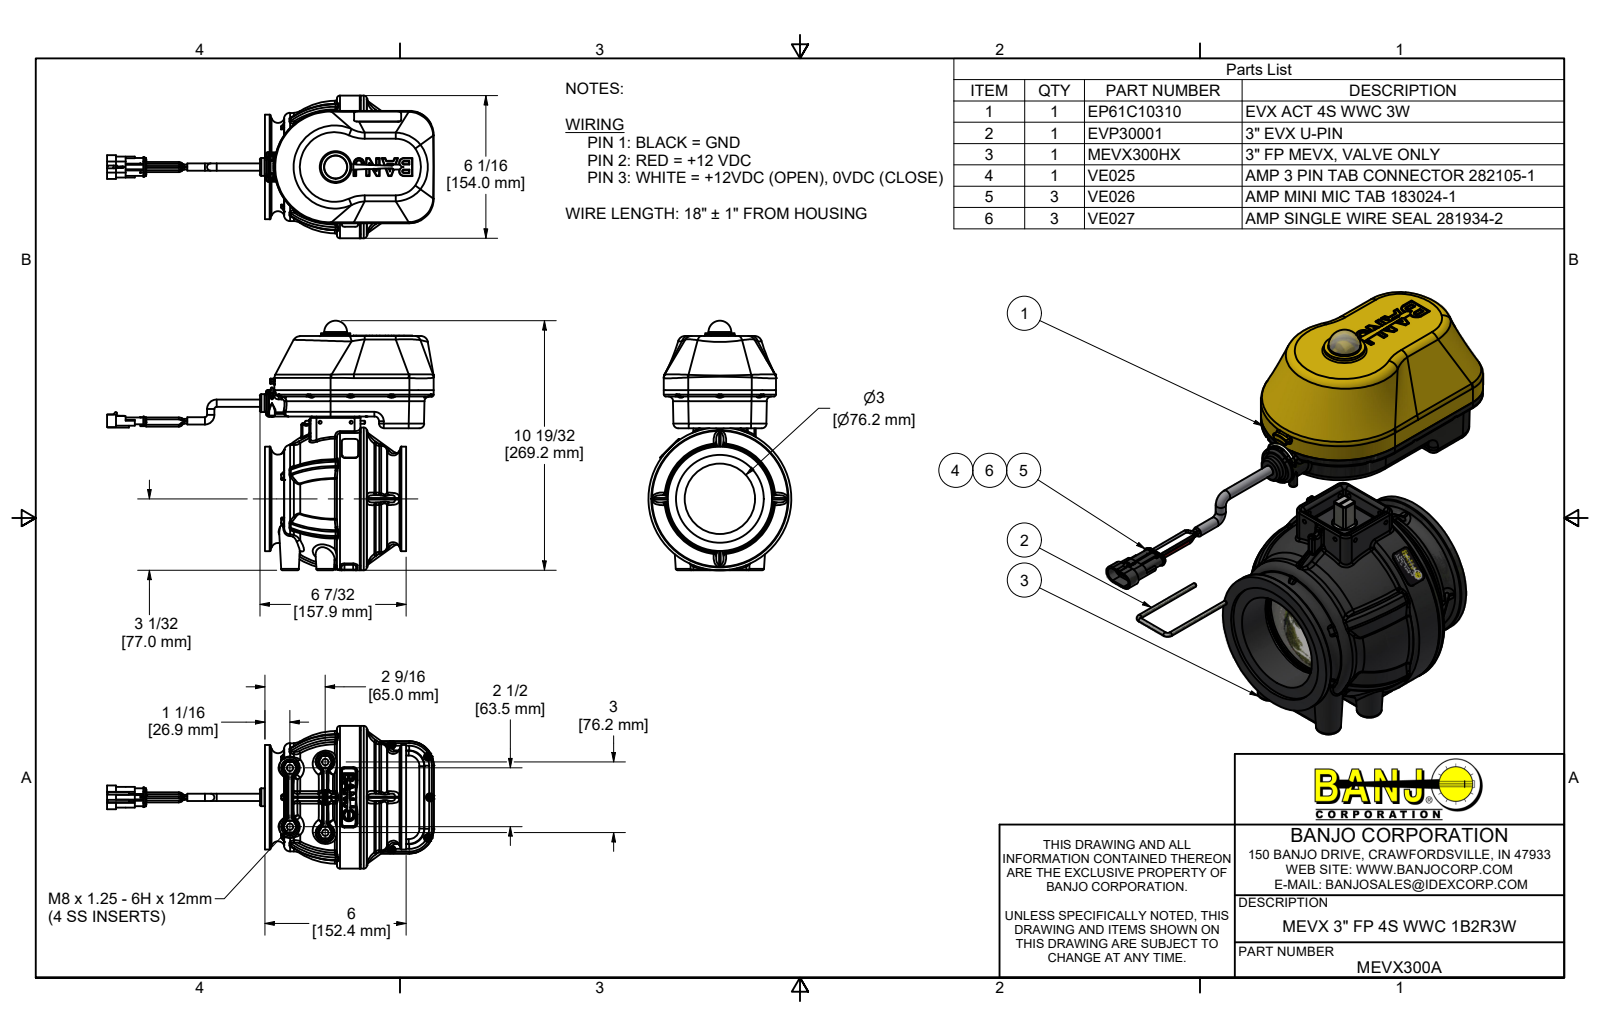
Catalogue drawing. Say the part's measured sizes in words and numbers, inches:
The part is named "MEVX300A; EP61C10310; B61905PPHS; B632038PM (+8 more)". Its 3-D file was written by "Autodesk Inventor 2022 (AUTOMOTIVE_DESIGN)". It is 86 solids with 9011 faces: 3301 planar, 3355 cylindrical and 2355 other. Overall it measures 13.88 by 10.6 by 6.063 inches. Its volume is 90.09 cubic inches and its surface area 904.7 square inches. Round holes: 15 of diameter 0.15, 11 of diameter 0.095, 11 of diameter 0.34, 7 of diameter 0.08, 6 of diameter 0.135, 4 of diameter 0.104, 4 of diameter 0.136, 4 of diameter 0.176, 4 of diameter 0.262, 4 of diameter 0.266, 4 of diameter 0.433, 3 of diameter 0.055. Round bosses or shafts: 19 of diameter 0.25, 15 of diameter 0.08, 11 of diameter 0.14, 11 of diameter 0.108, 11 of diameter 0.085, 6 of diameter 0.058, 5 of diameter 0.375, 4 of diameter 0.437. Partial cylindrical surfaces (rounded edges, fillets, slot ends): 204 of radius 0.013, 138 of radius 0.405, 114 of radius 0.387, 112 of radius 0.309, 111 of radius 0.01, 108 of radius 0.253, 106 of radius 0.609, 46 of radius 0.04. The main face-to-face distances are 0.083, 0.5, 0.085, 0.125, 0.181, 0.096, 2.175, 2.356, 2.271, 2.481. The hole center spacings are 1.69, 2.272, 3.257, 3.316, 0.998, 1.313, 1.465, 2.315.
